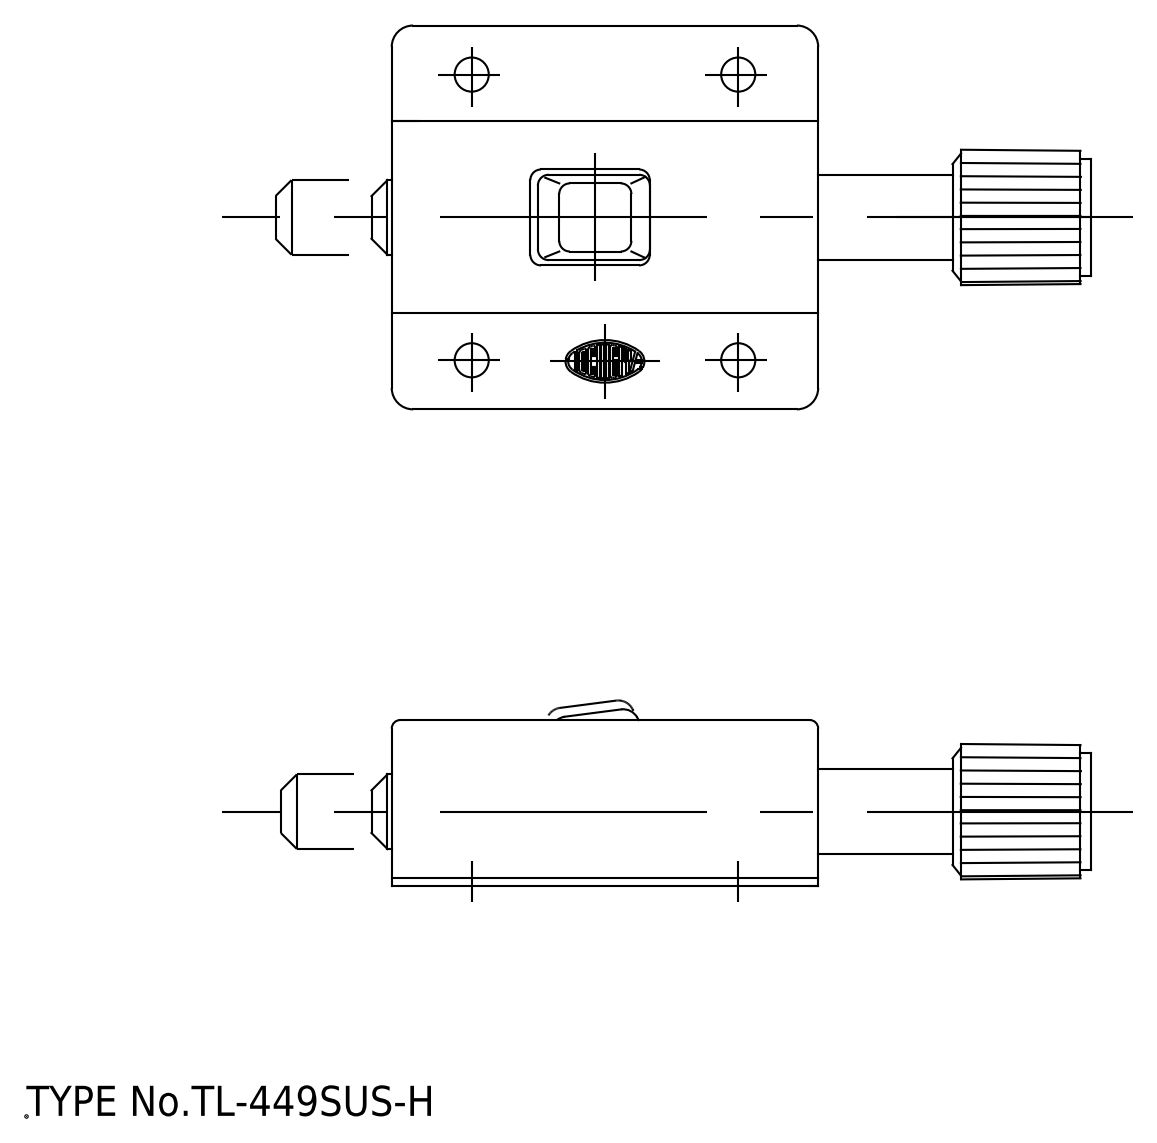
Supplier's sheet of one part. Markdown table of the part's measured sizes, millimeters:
| quantity | value |
| --- | --- |
| part name | ケース; ロックボルト |
| STEP written by | spGate 19.8.4 (****-****-****-****) (AUTOMOTIVE_DESIGN) |
| units | millimeters |
| bodies | 2 solids, 91 faces (35 planar, 46 cylindrical, 10 other) |
| overall size | 67.5 × 36 × 16.61 |
| volume | 6 501 mm³ |
| surface area | 8 429 mm² |
| round holes (diameter × count) | 3.2 × 4, 8 × 1 |
| round bosses / shafts (diameter × count) | 11 × 1, 7 × 1 |
| partial cylindrical surfaces (radius × count) | 2 × 6, 0.5 × 4, 0.8 × 2, 0.95 × 2, 1.2 × 2, 1.5 × 2, 1.75 × 2 |
| main face-to-face distances | 0.8, 14.8, 17.2, 14, 15.6, 18, 16.4, 39.2, 30.7, 8.5 |
| hole center spacings | 25, 26.8, 36.65 |
